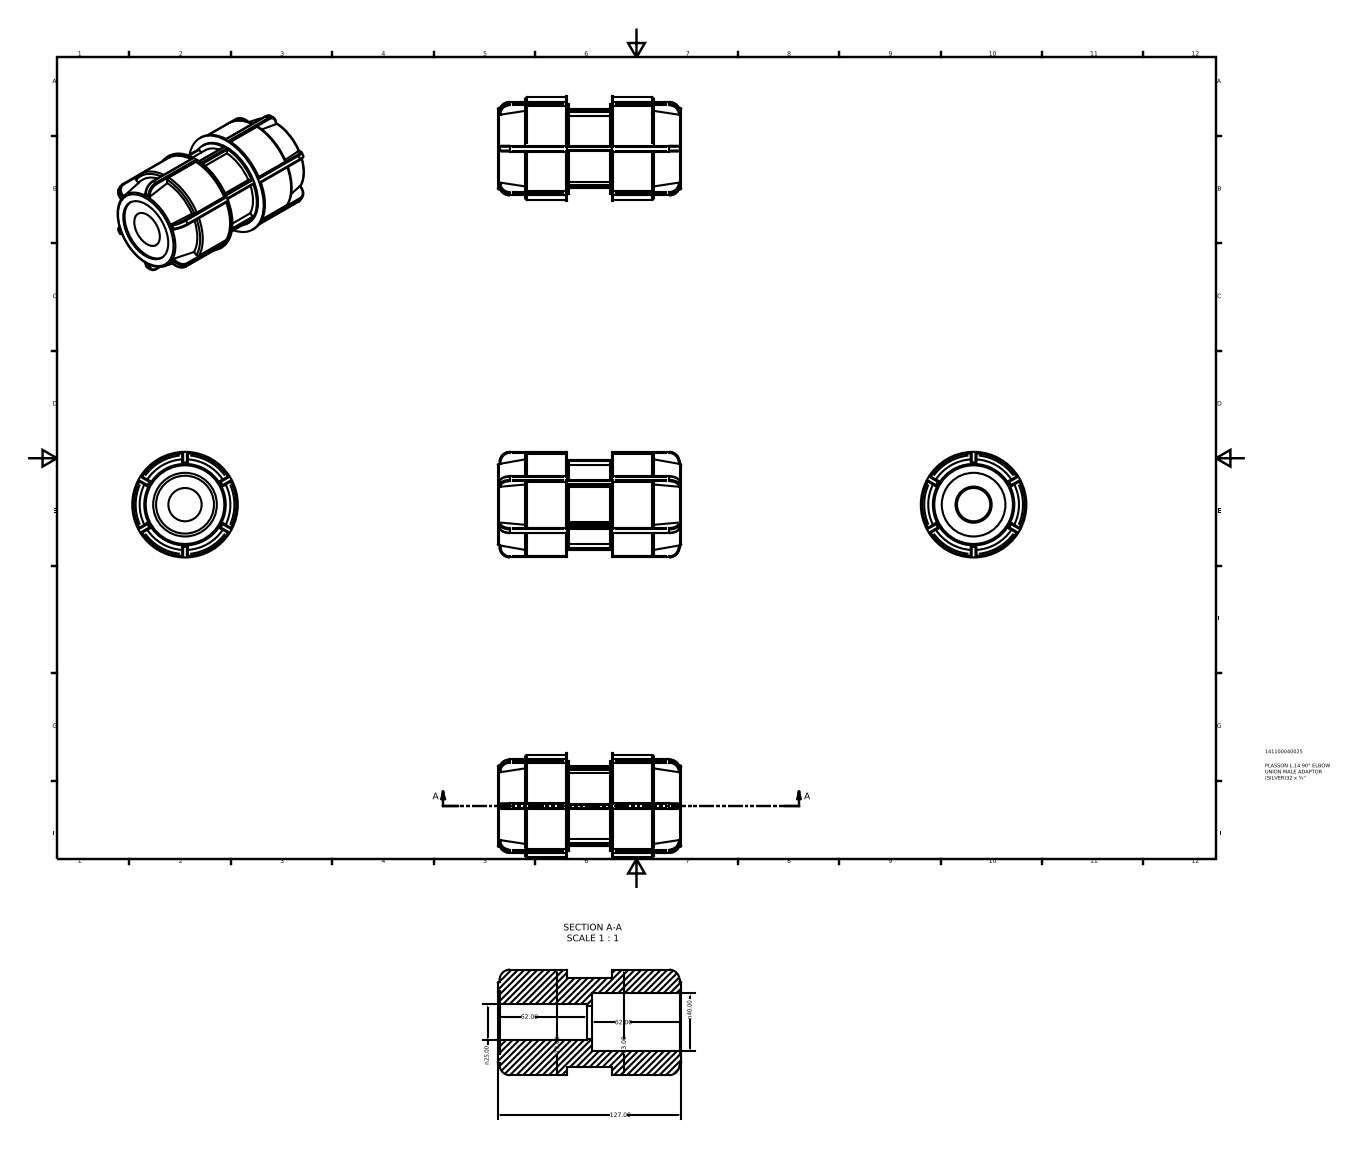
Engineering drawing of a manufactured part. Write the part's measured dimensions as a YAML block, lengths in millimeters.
part_name: "141100040025"
step_written_by: "Autodesk Inventor 2015 (AUTOMOTIVE_DESIGN)"
units: millimeters
bodies: {solids: 1, faces: 230, planar: 92, cylindrical: 86, other: 52}
overall_size: [127, 73, 73]
volume: 306997
surface_area: 52083
round_holes:
  - {diameter: 23, count: 1}
  - {diameter: 25, count: 1}
  - {diameter: 40, count: 1}
  - {diameter: 44, count: 1}
round_bosses_or_shafts:
  - {diameter: 73, count: 1}
  - {diameter: 70.81, count: 1}
  - {diameter: 62.05, count: 1}
  - {diameter: 54.75, count: 1}
partial_cylinders:
  - {radius: 0.73, count: 44}
face_to_face_distances: [1.27, 30.48, 77.47, 48.26, 29.21, 78.74, 46.99, 4, 49.53, 125.73]
